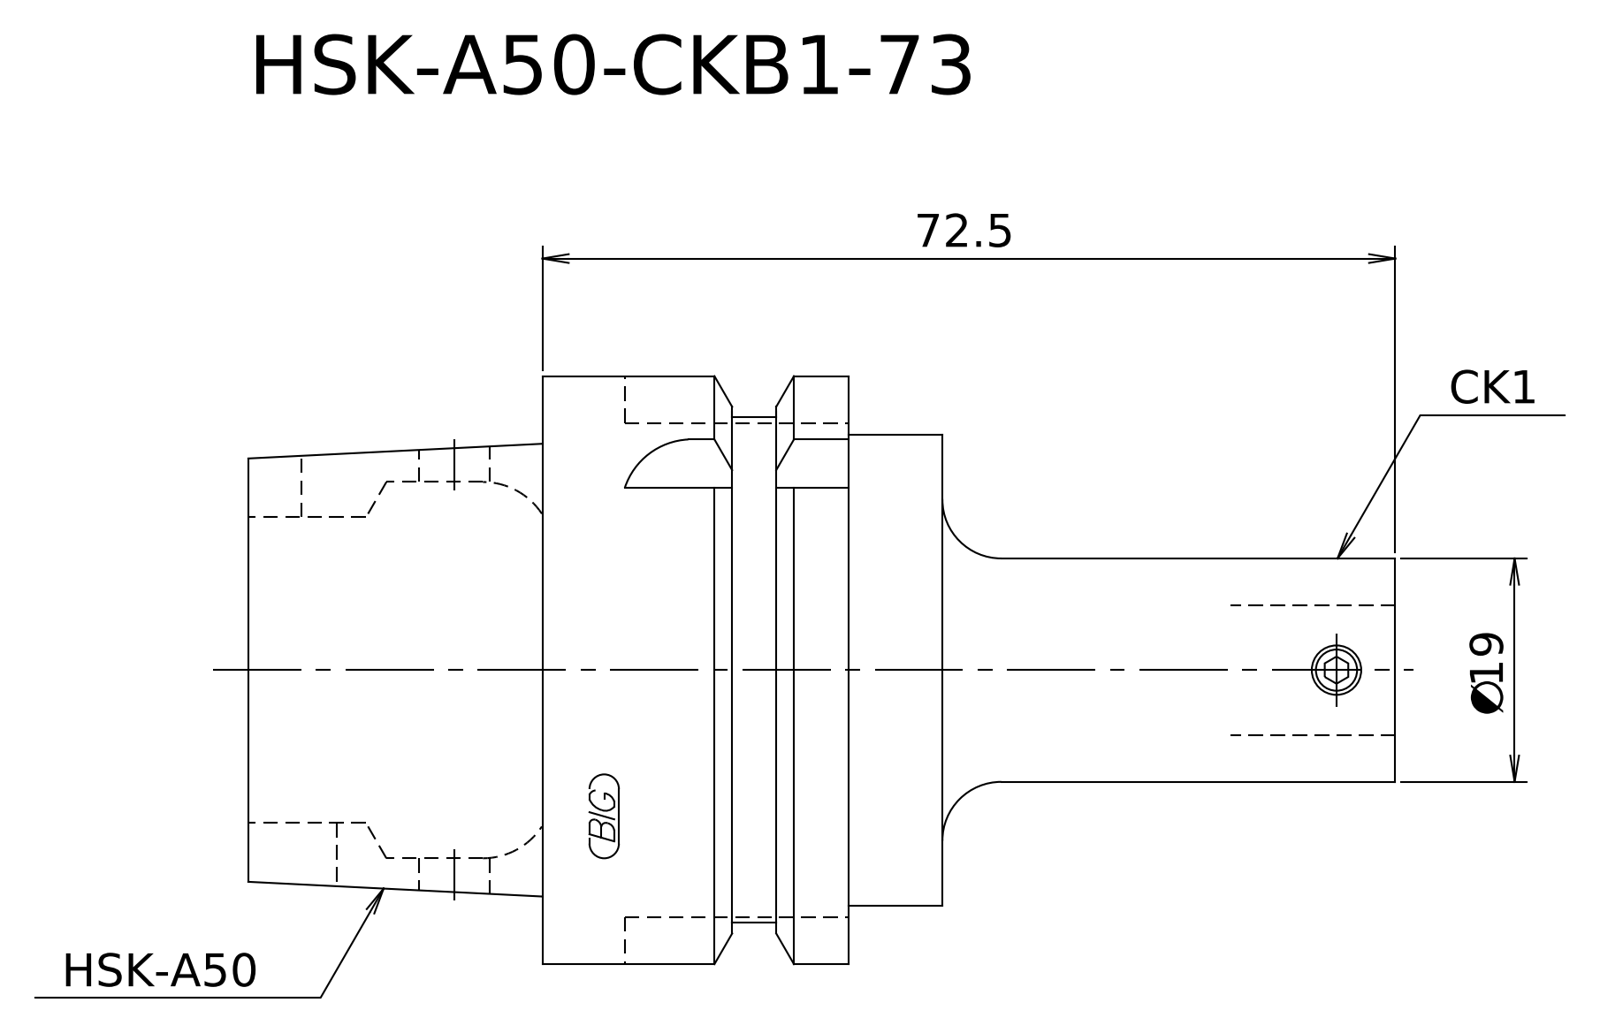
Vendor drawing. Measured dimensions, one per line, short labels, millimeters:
written by: Kubotek KeyCreator V8.5.1 (14335) (CONFIG_CONTROL_DESIGN)
unit: mm
bodies: 1 solid, 17 faces (7 planar, 6 cylindrical, 4 other)
size: 97.5 × 50 × 50
volume: 97 630 mm³; area: 14 554 mm²
bosses: 1× ⌀50, 1× ⌀43, 1× ⌀40, 1× ⌀38.3, 1× ⌀19
face distances: 25, 26, 51, 8, 34, 59, 38.5, 46.5, 72.5, 97.5
